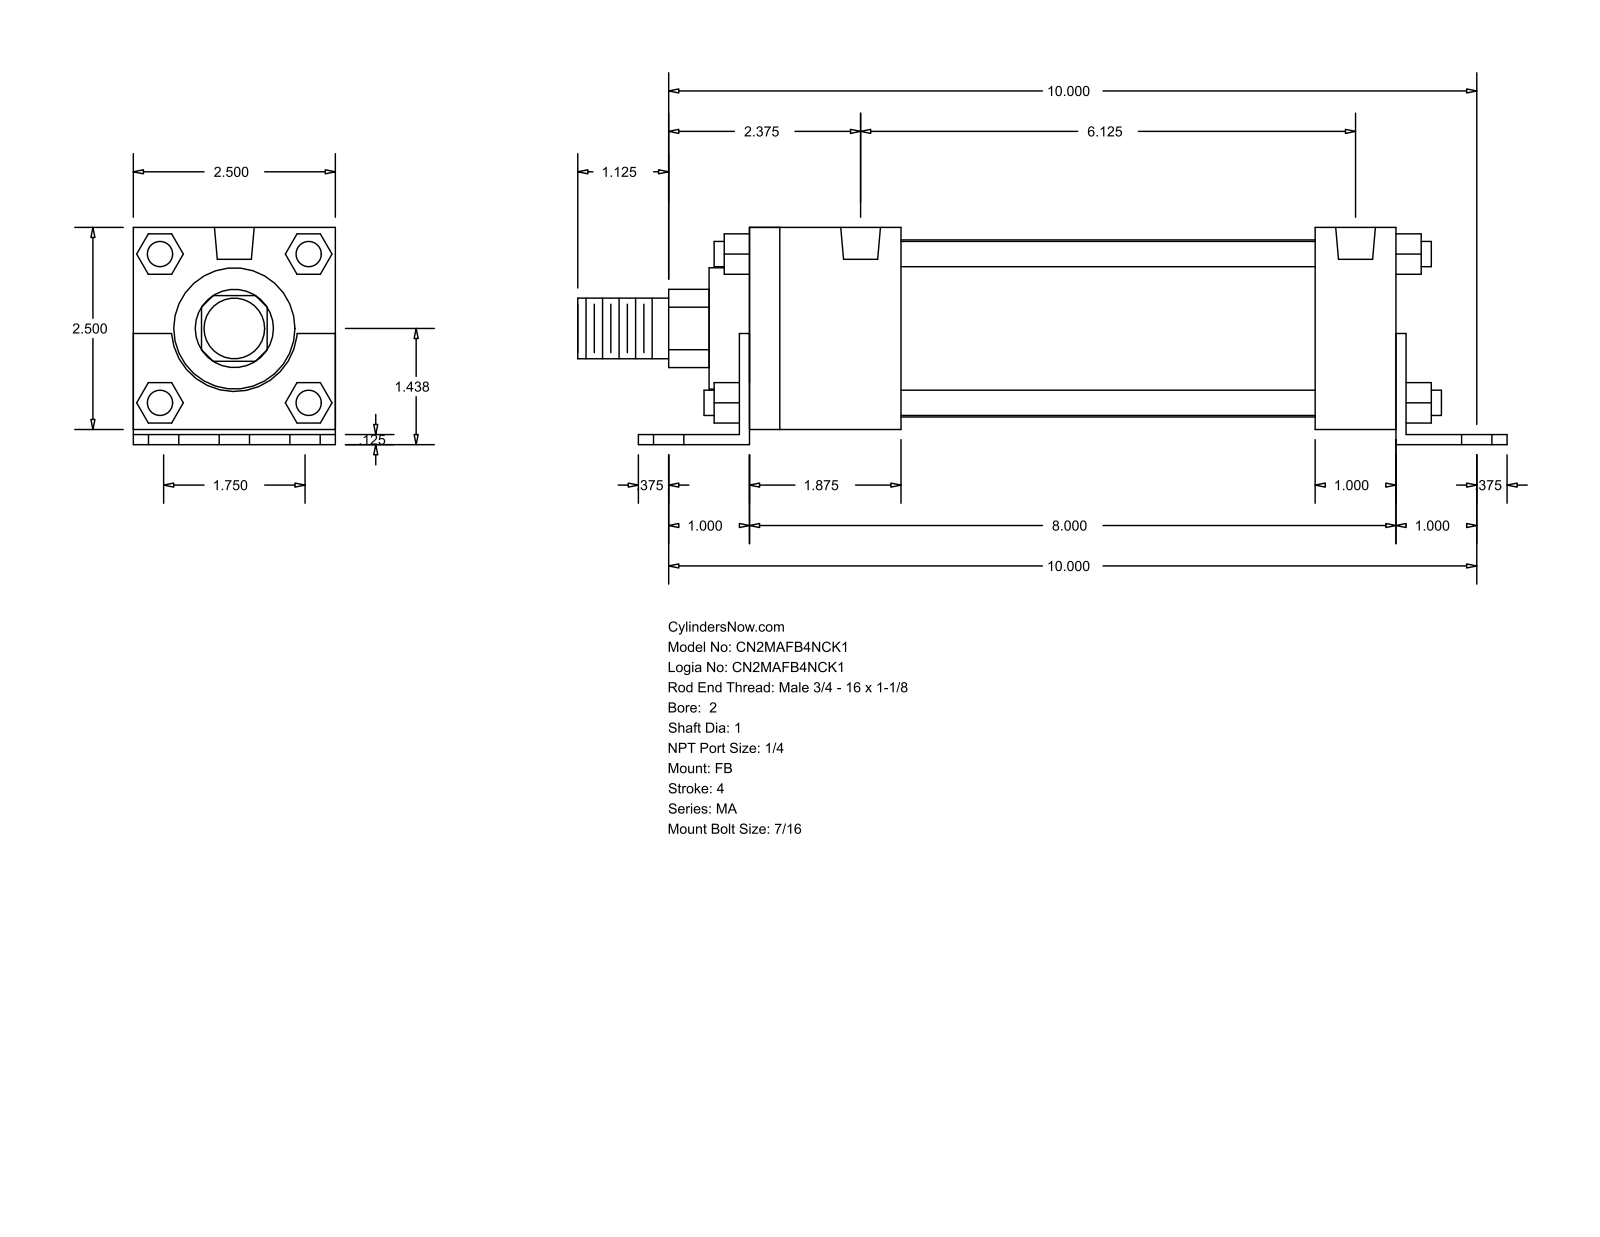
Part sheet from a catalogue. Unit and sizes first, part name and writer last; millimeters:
Units: millimetres
Overall size (bounding box): 292.1 × 68.26 × 63.5
Round holes (diameter × count): ⌀11.11 ×6, ⌀7.94 ×4, ⌀12.49 ×2
Round bosses / shafts (diameter × count): ⌀7.94 ×4, ⌀55.63 ×1, ⌀38.1 ×1, ⌀25.4 ×1, ⌀19.05 ×1
Partial cylindrical surfaces — rounded edges, fillets, slot ends (radius × count): R12.29 ×1, R19.81 ×1
Main face-to-face distances: 63.5, 3.17, 4.76, 68.26, 1.59, 65.09, 12.7, 3.18, 203.2, 206.38
Hole centre spacings: 22.23, 254.97, 254, 44.11, 44.46, 64.3, 155.57, 194.94
Bodies: 0 solids, 140 faces (105 planar, 35 cylindrical, 0 other)
Part name (STEP PRODUCT): MA_FB__0200_1
STEP written by: GSSL Pune (CONFIG_CONTROL_DESIGN)
